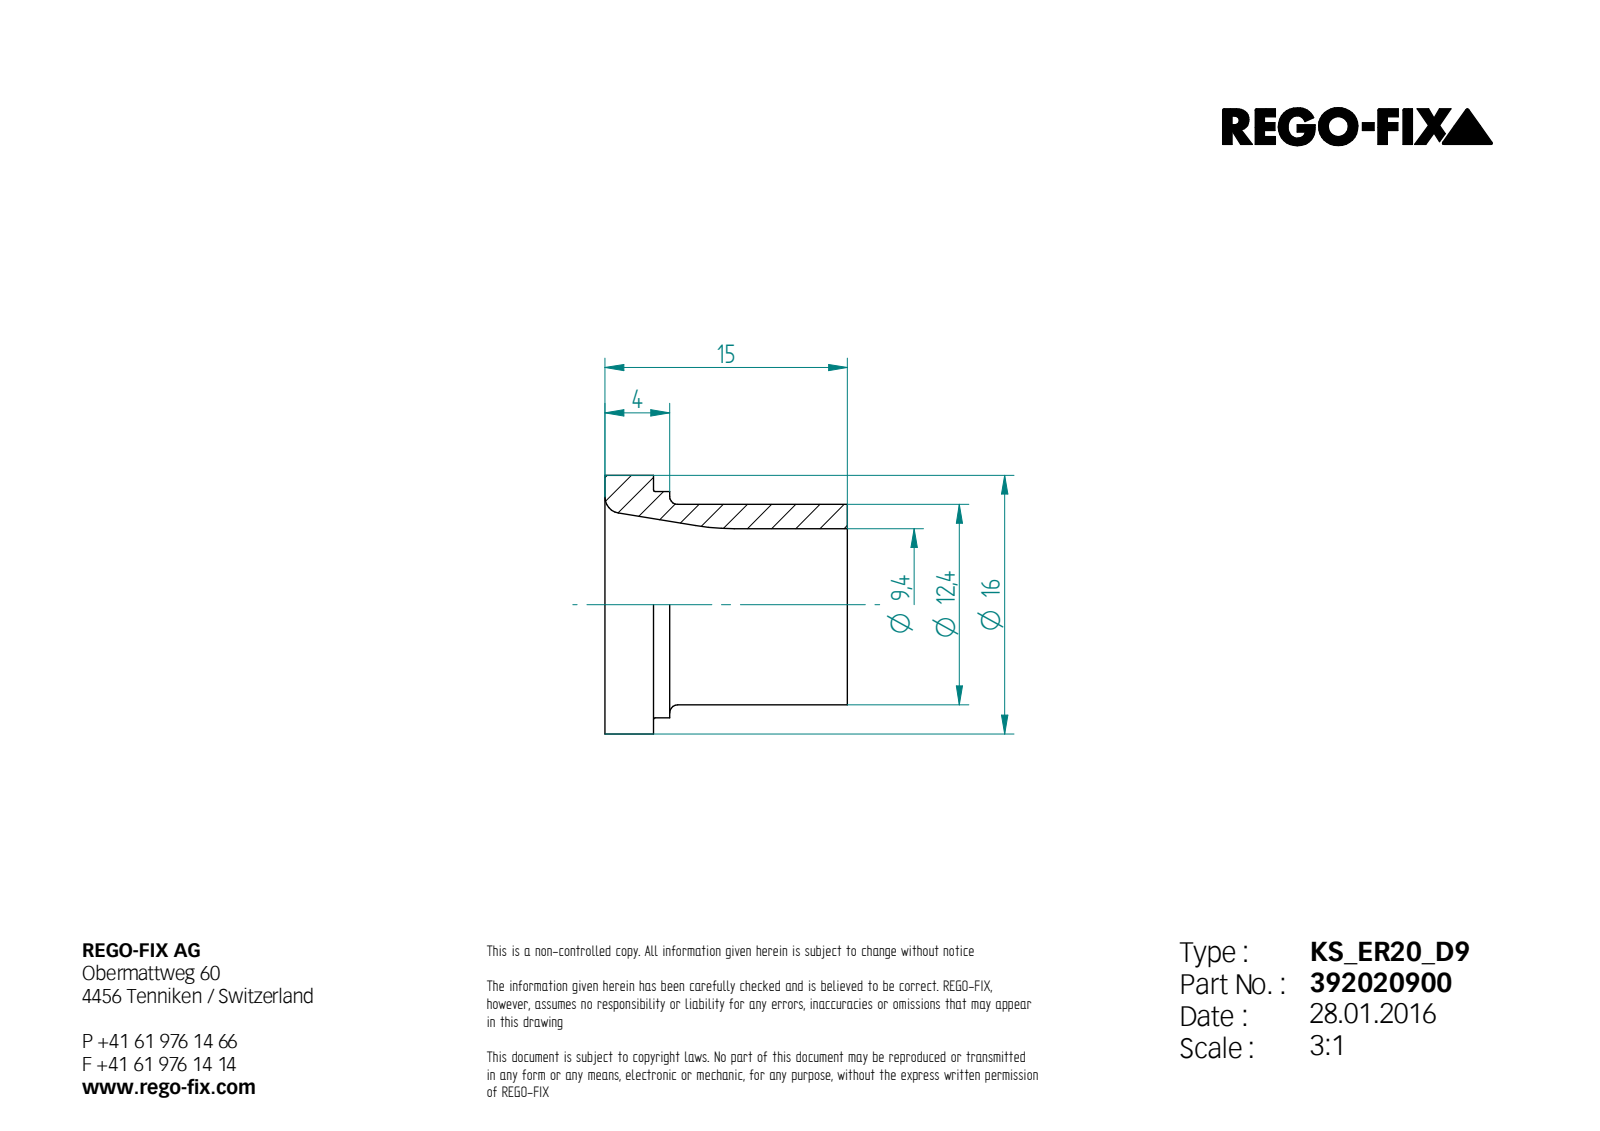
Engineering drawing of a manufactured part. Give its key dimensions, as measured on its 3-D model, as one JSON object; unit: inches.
{"step_written_by": "Unknown (AUTOMOTIVE_DESIGN)", "units": "inches", "bodies": {"solids": 1, "faces": 13, "planar": 4, "cylindrical": 4, "other": 5}, "overall_size": [0.63, 0.63, 0.591], "volume_in3": 0.056, "surface_area_in2": 2.013, "round_holes": [[0.37, 1]], "round_bosses_or_shafts": [[0.63, 1], [0.551, 1], [0.488, 1]], "face_to_face_distances": [0.591, 0.118, 0.472, 0.157, 0.039, 0.433]}
